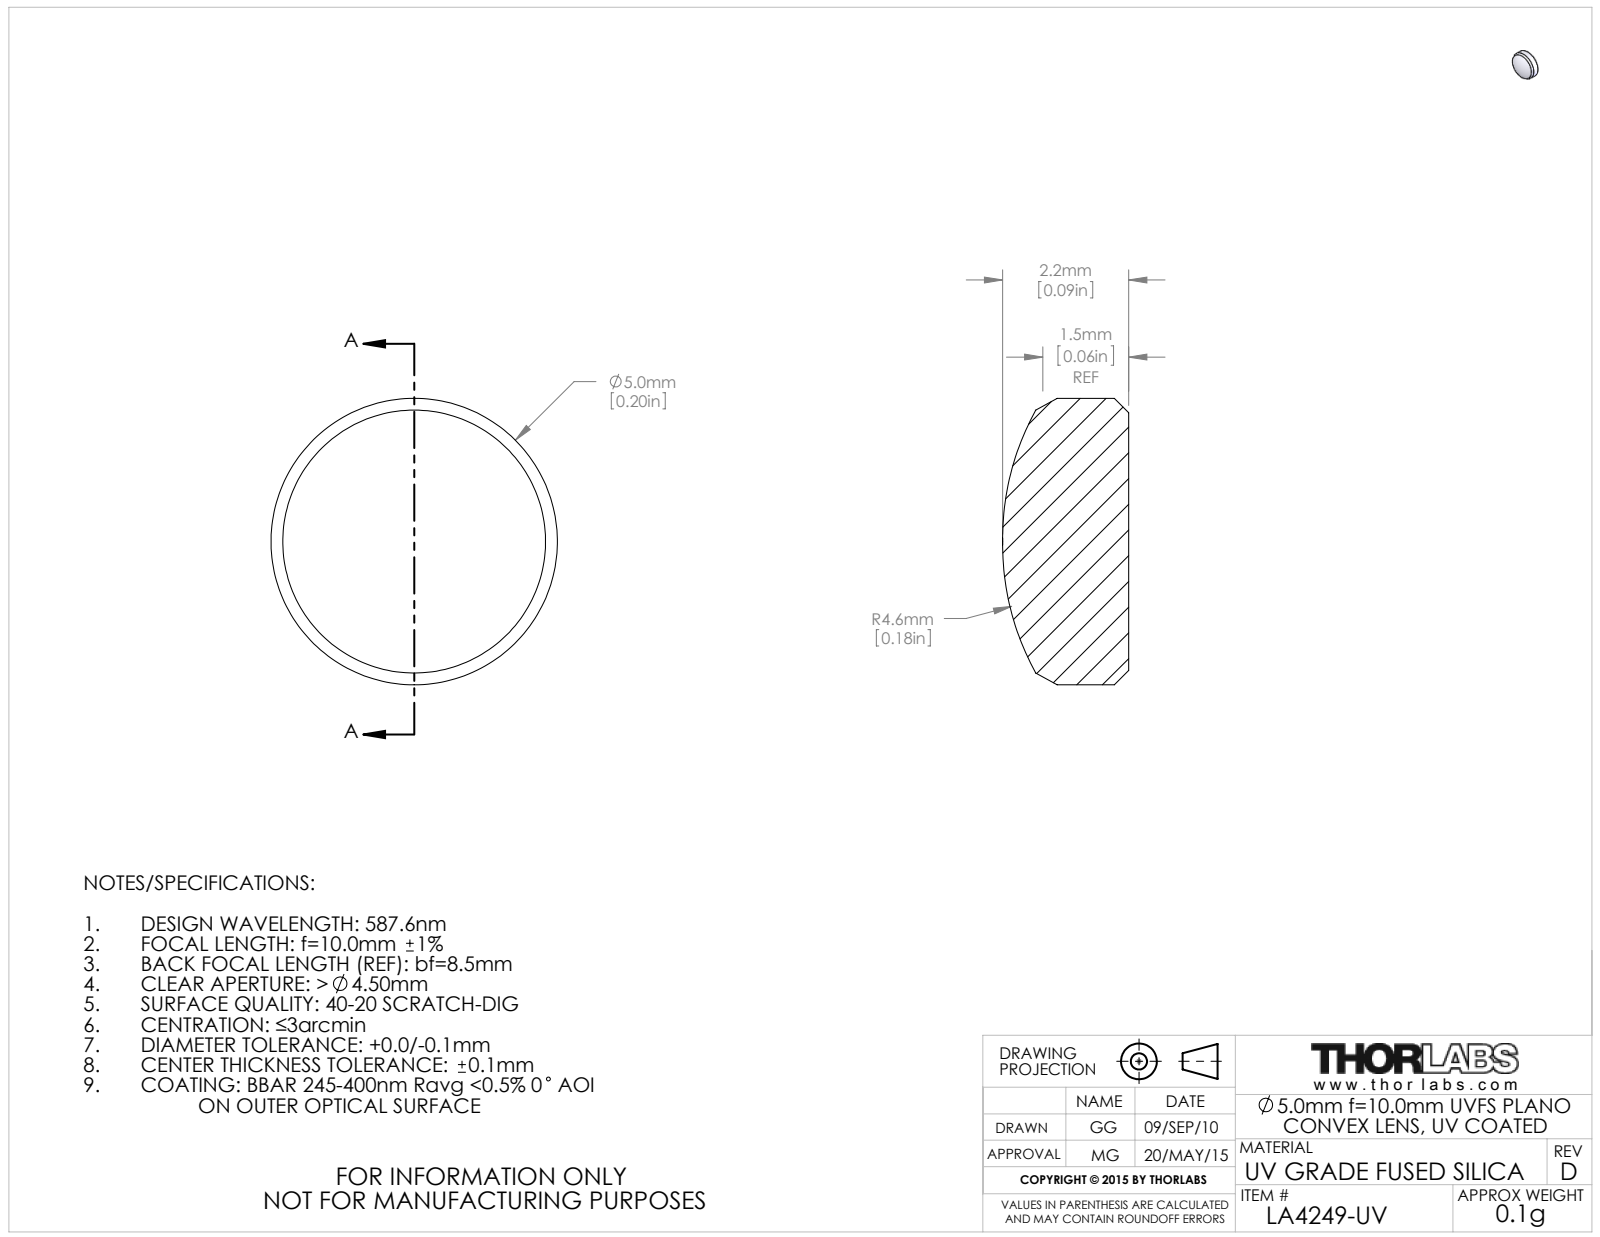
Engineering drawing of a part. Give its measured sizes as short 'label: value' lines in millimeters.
name: 4267-E0W
written by: SolidWorks 2014 (CONFIG_CONTROL_DESIGN)
unit: mm
bodies: 1 solid, 9 faces (1 planar, 2 cylindrical, 6 other)
size: 5 × 5 × 2.2
volume: 36 mm³; area: 61 mm²
bosses: 1× ⌀5
